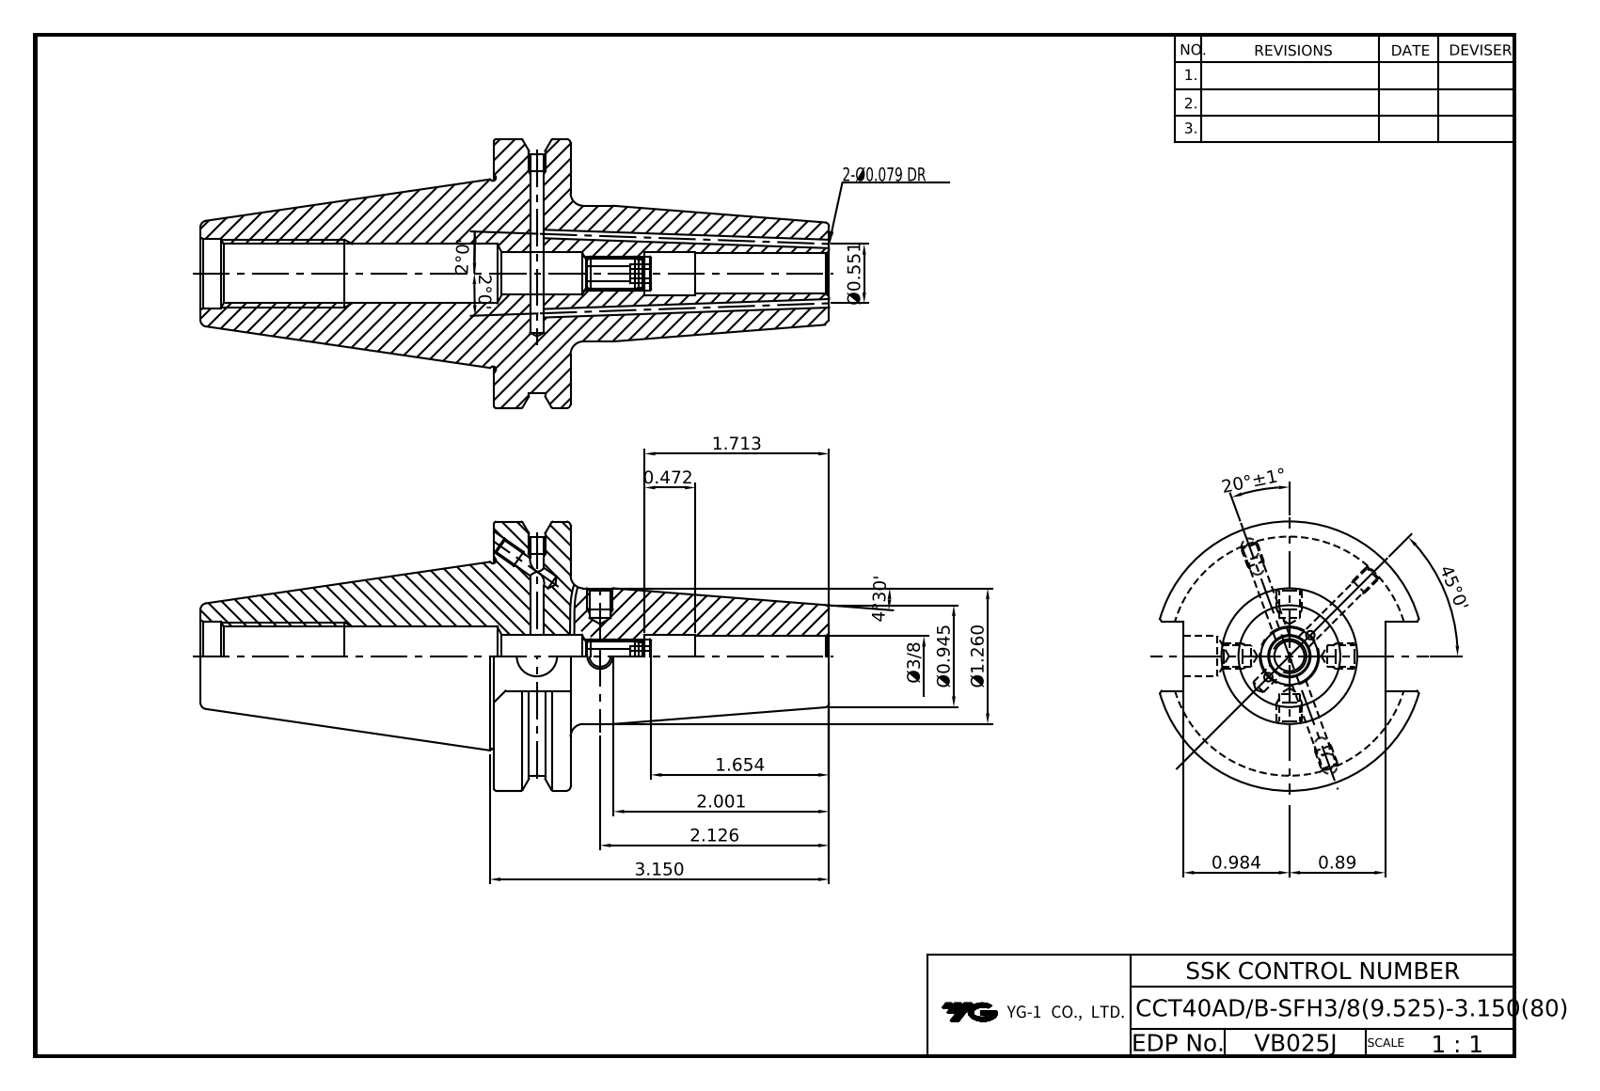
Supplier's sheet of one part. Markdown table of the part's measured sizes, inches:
| quantity | value |
| --- | --- |
| part name | LO-CCT40ADB-SFH3_8C-3_15 |
| STEP written by | CREO PARAMETRIC BY PTC INC, 2018100 (CONFIG_CONTROL_DESIGN) |
| units | inches |
| bodies | 1 solid, 152 faces (48 planar, 64 cylindrical, 40 other) |
| overall size | 5.837 × 2.5 × 2.402 |
| volume | 8.519 in³ |
| surface area | 46.43 in² |
| round holes (diameter × count) | 0.157 × 7, 0.134 × 3, 0.375 × 2, 0.276 × 1, 0.315 × 1, 0.394 × 1, 0.398 × 1, 0.531 × 1, 0.551 × 1, 0.625 × 1, 0.642 × 1 |
| round bosses / shafts (diameter × count) | 2.5 × 1, 1.724 × 1, 1.26 × 1 |
| partial cylindrical surfaces (radius × count) | 1.108 × 1 |
| main face-to-face distances | 0.711, 3.11, 2.4, 1.874, 2.726, 3.437, 5.837, 0.645, 0.189, 2.537 |
